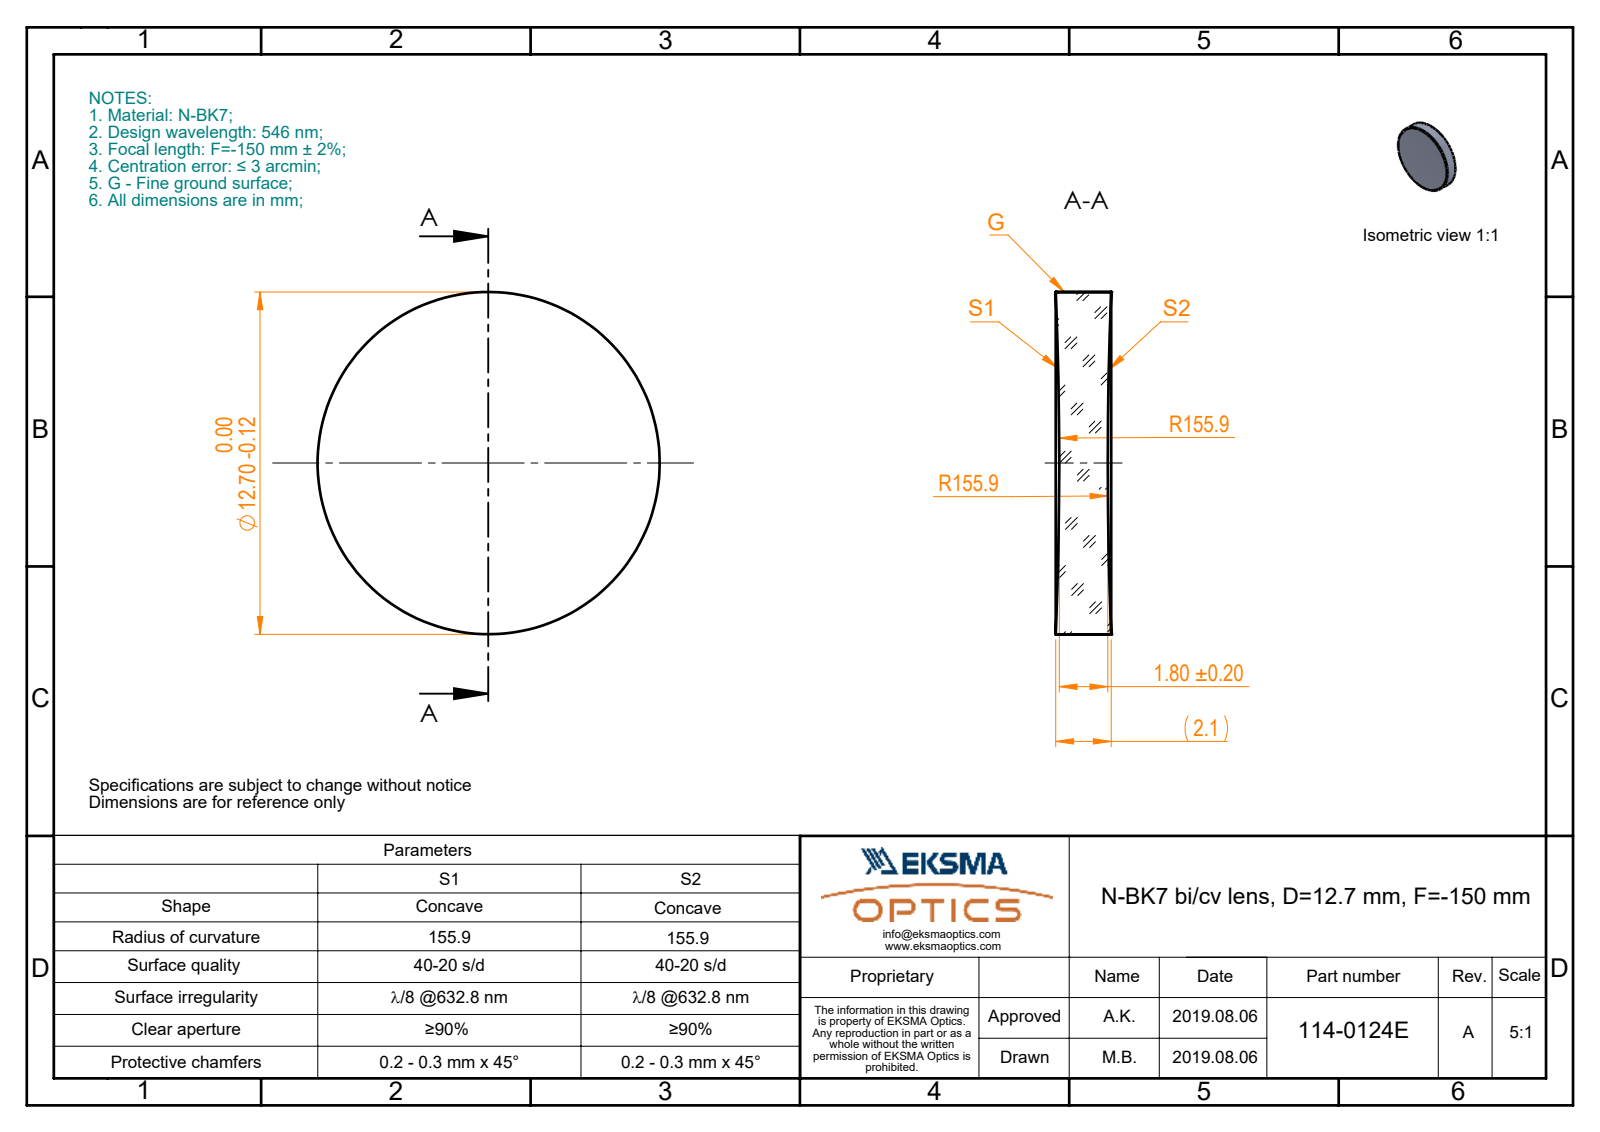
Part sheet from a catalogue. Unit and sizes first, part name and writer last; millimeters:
Units: millimetres
Overall size (bounding box): 12.7 × 12.7 × 2.06
Round bosses / shafts (diameter × count): ⌀12.7 ×1
Volume: 244 mm³ · Surface area: 336 mm²
Bodies: 1 solid, 6 faces (0 planar, 2 cylindrical, 4 other)
Part name (STEP PRODUCT): 114-0124E BK7 bi-cv 12.7 F-150
STEP written by: SolidWorks 2017 (CONFIG_CONTROL_DESIGN)
